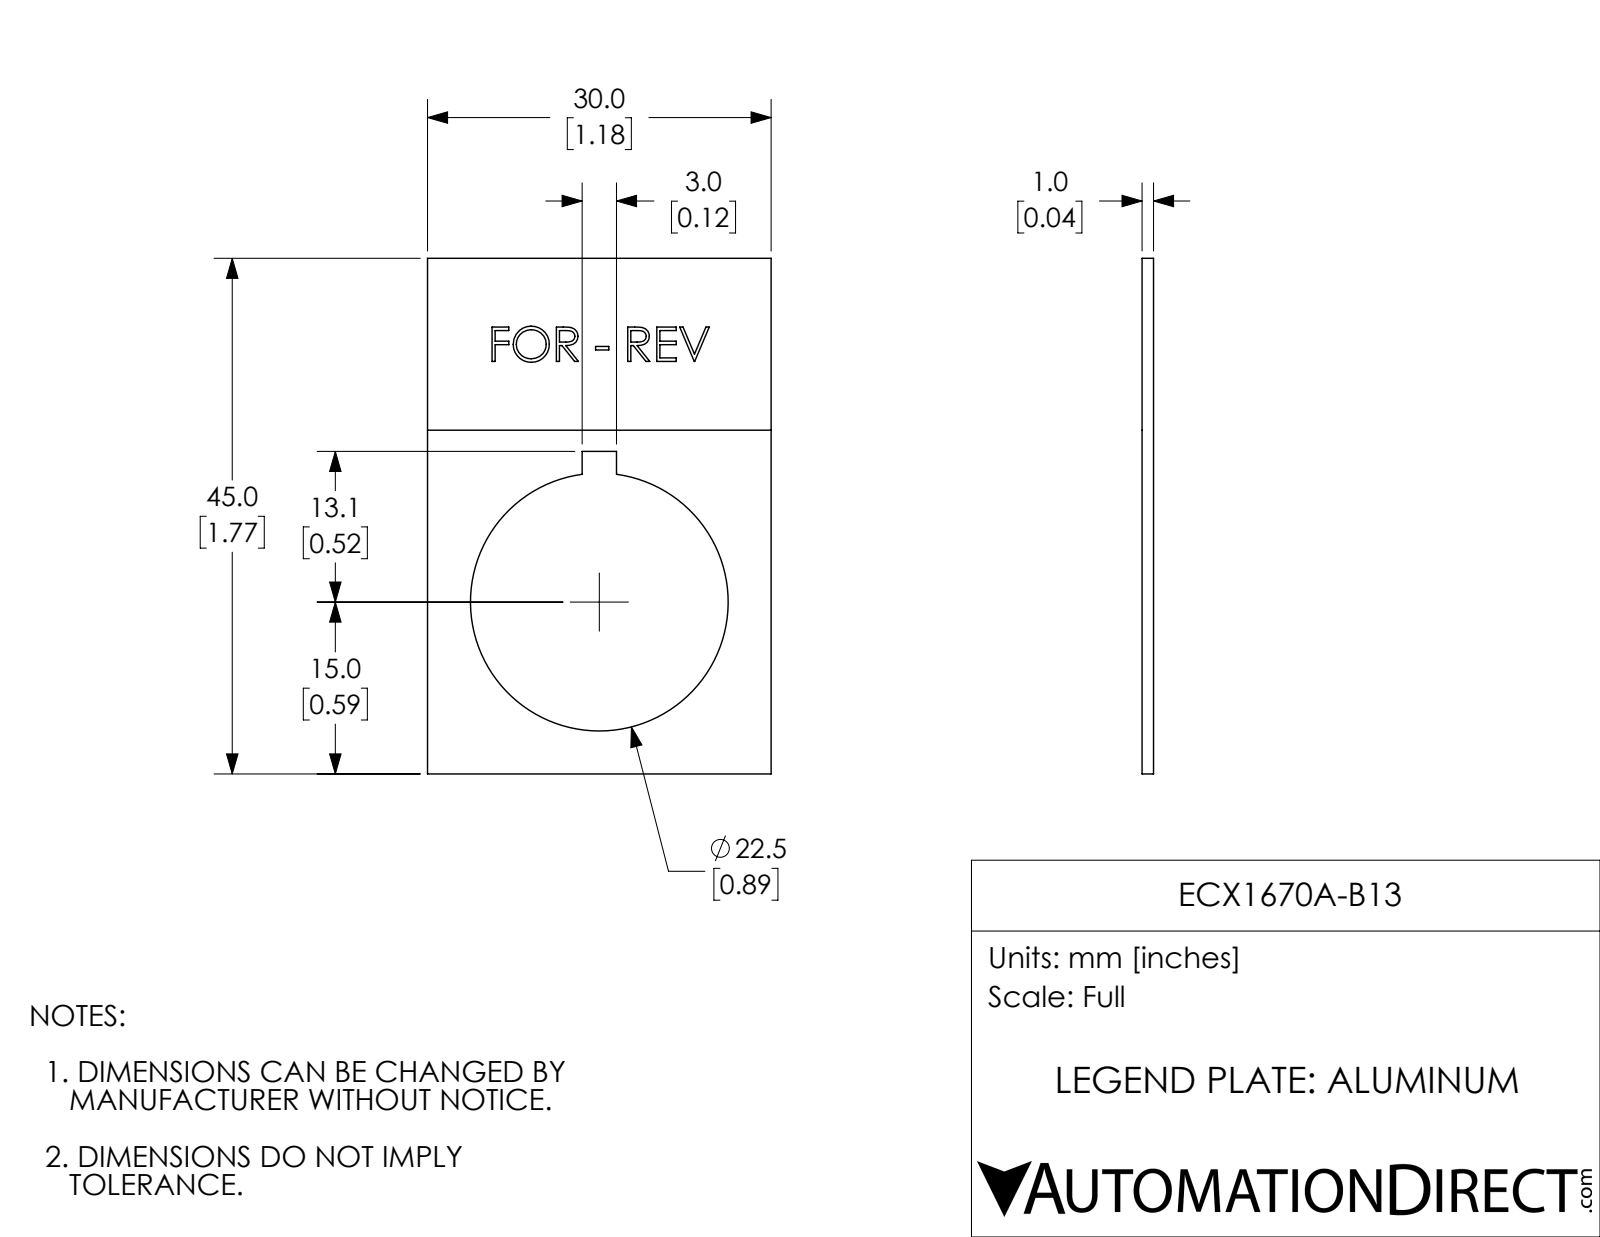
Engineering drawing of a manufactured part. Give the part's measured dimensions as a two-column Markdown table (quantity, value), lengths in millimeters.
| quantity | value |
| --- | --- |
| part name | ECX1670A-B13 |
| STEP written by | SolidWorks 2017 (AUTOMOTIVE_DESIGN) |
| units | millimeters |
| bodies | 1 solid, 96 faces (75 planar, 3 cylindrical, 18 other) |
| overall size | 45 × 30 × 1 |
| volume | 950 mm³ |
| surface area | 2 120 mm² |
| round holes (diameter × count) | 22.5 × 1 |
| main face-to-face distances | 1, 30, 45, 1, 13.5, 16.5, 28.1, 16.8, 3, 0.3 |
